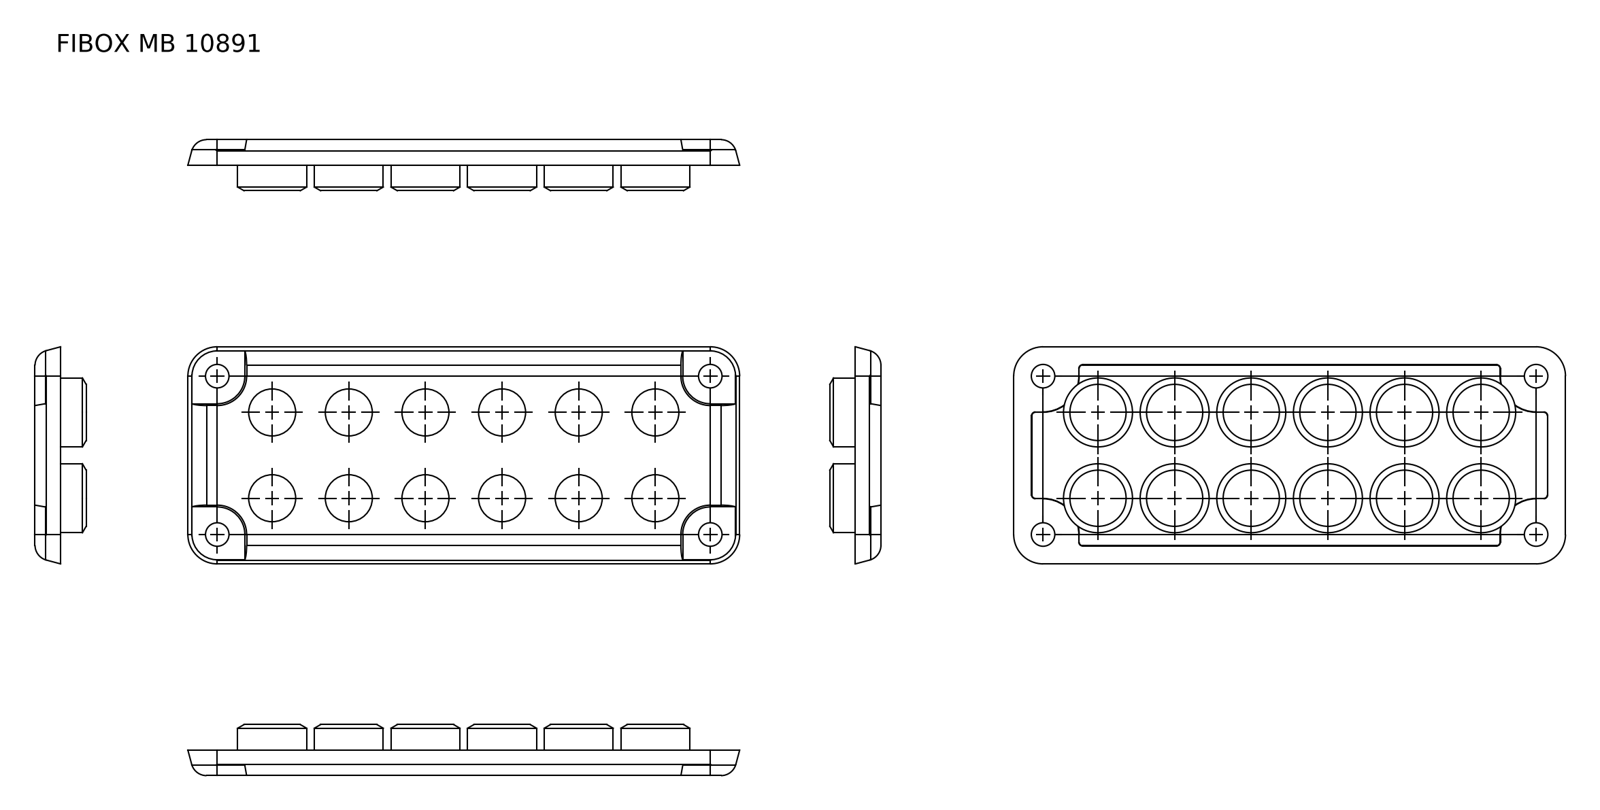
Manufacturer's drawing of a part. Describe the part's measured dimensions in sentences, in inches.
The part is named "FIBOX MB10891". Its 3-D file was written by "SolidWorks 2014 (AUTOMOTIVE_DESIGN)". It is 1 solid with 163 faces: 55 planar, 60 cylindrical and 48 other. Overall it measures 8.504 by 3.346 by 0.787 inches. Its volume is 8.384 cubic inches and its surface area 109.7 square inches. Round holes: 12 of diameter 0.724, 4 of diameter 0.362. Round bosses or shafts: 12 of diameter 1.063. Partial cylindrical surfaces (rounded edges, fillets, slot ends): 4 of radius 0.236. The main face-to-face distances are 0.394, 0.118, 0.276, 0.669, 0.787, 0.157, 0.63, 0.236, 0.512, 0.472. The hole center spacings are 1.181, 1.773, 2.362, 2.707, 1.323, 3.543, 3.782, 1.015.
